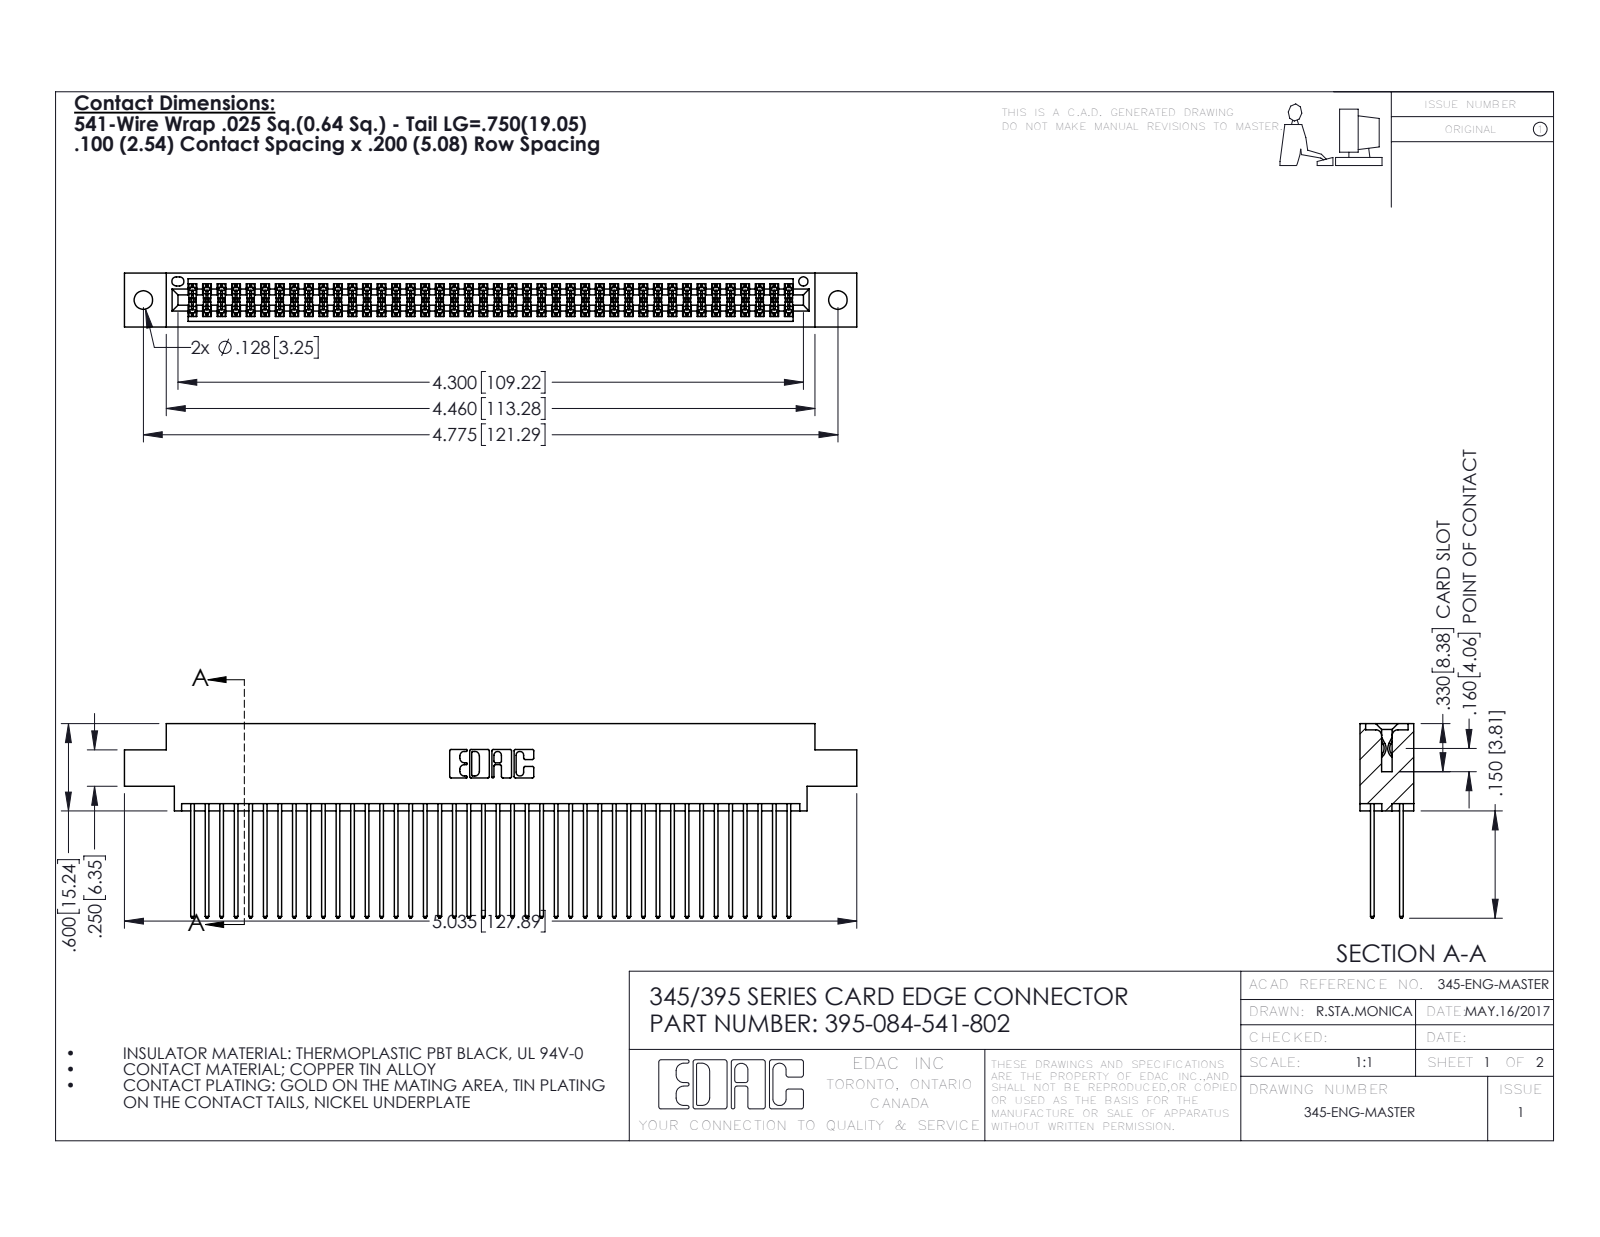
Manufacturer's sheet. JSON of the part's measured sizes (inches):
{"part_name": "395-084-541-802; 345-292-001_345-293-141; 345 Part_0.170 Offset - 0.128 Dia", "step_written_by": "SolidWorks 2016 (CONFIG_CONTROL_DESIGN)", "units": "inches", "bodies": {"solids": 85, "faces": 4330, "planar": 2856, "cylindrical": 1474, "other": 0}, "overall_size": [5.035, 1.337, 0.37], "volume_in3": 0.778, "surface_area_in2": 32.54, "round_holes": [[0.128, 2], [0.064, 1]], "partial_cylinders_radius": [[0.006, 126], [0.01, 84], [0.01, 22], [0.007, 6], [0.031, 6], [0.026, 3], [0.014, 2], [0.019, 2]], "face_to_face_distances": [0.298, 0.072, 0.2, 0.098, 0.272, 0.025, 0.37, 0.225, 0.175, 0.149], "hole_center_spacings": [0.27, 4.539, 4.775]}
